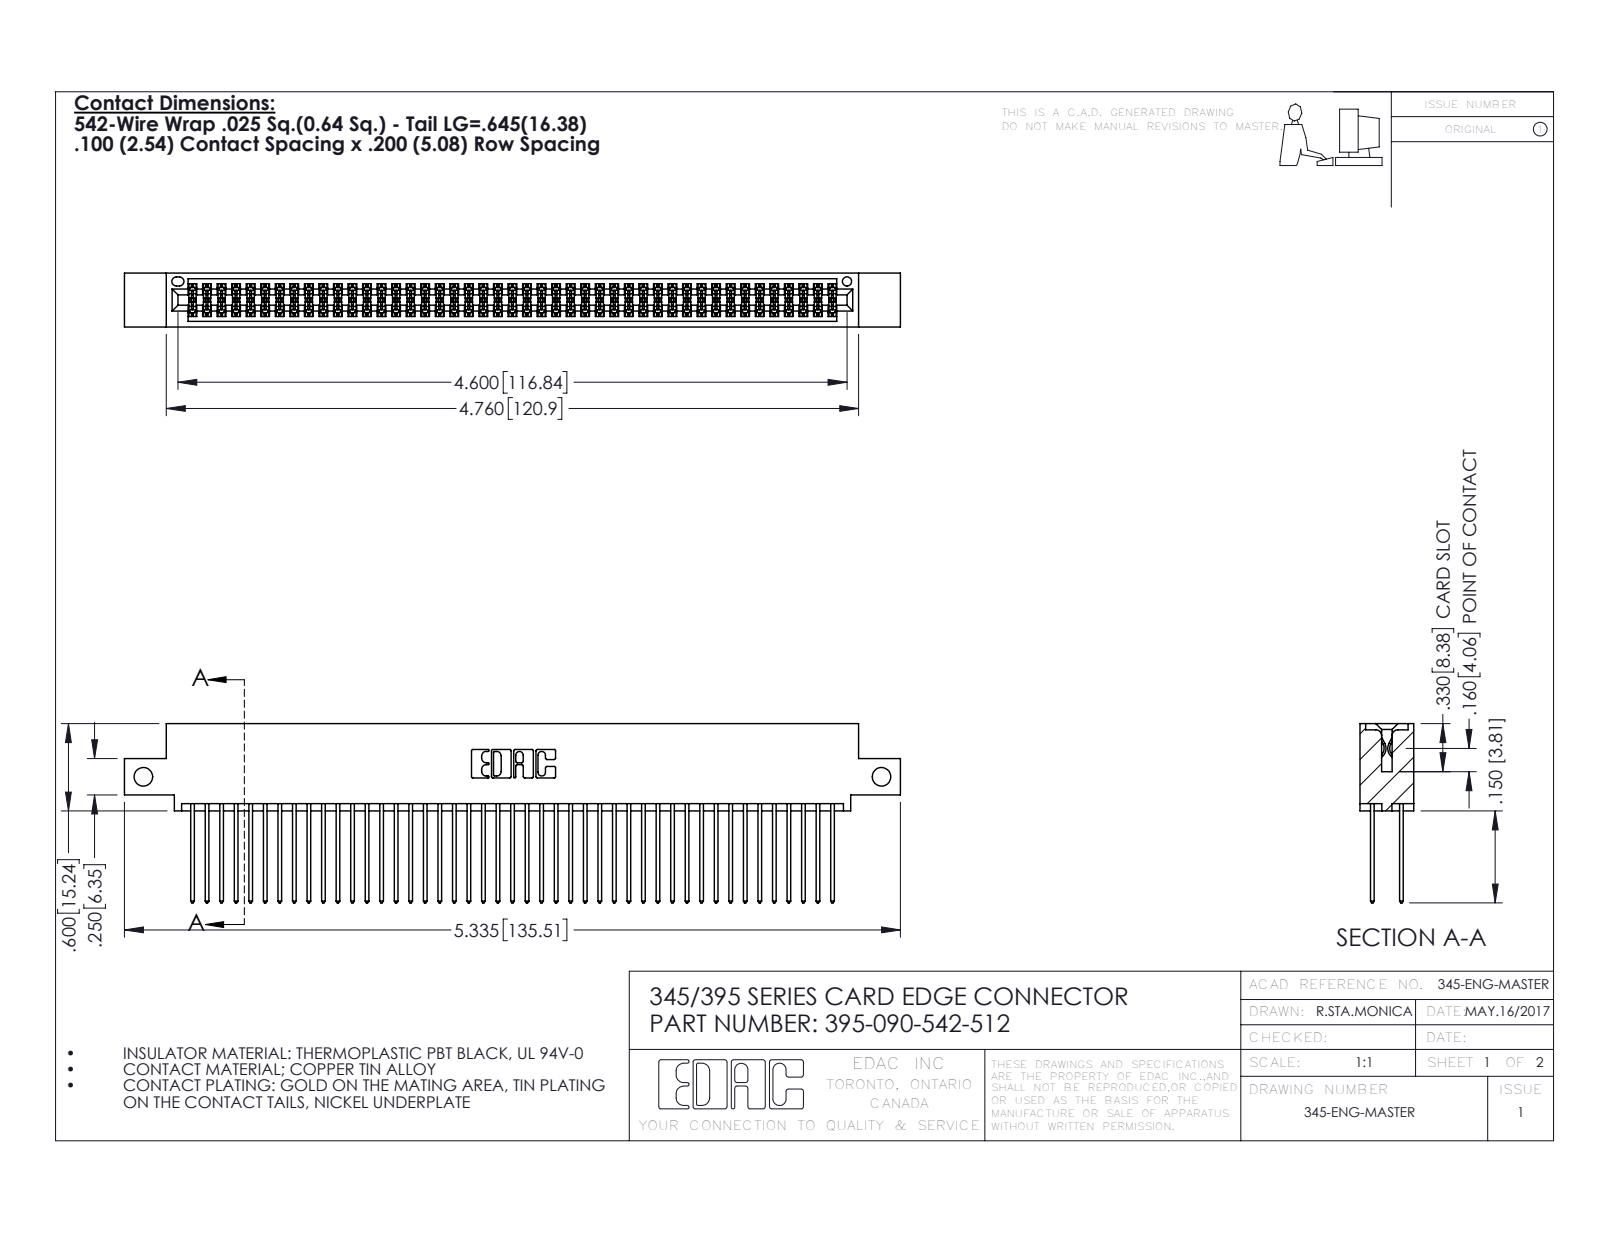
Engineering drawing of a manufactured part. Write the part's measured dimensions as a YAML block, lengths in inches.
part_name: "395-090-542-512; 345 Part_0.110 Offset - Side Mount; 345-292-001_345-293-142"
step_written_by: "SolidWorks 2016 (CONFIG_CONTROL_DESIGN)"
units: inches
bodies: {solids: 91, faces: 4630, planar: 3054, cylindrical: 1576, other: 0}
overall_size: [5.335, 1.232, 0.37]
volume: 0.821
surface_area: 33.88
round_holes:
  - {diameter: 0.128, count: 2}
  - {diameter: 0.064, count: 1}
partial_cylinders:
  - {radius: 0.006, count: 135}
  - {radius: 0.01, count: 90}
  - {radius: 0.01, count: 22}
  - {radius: 0.007, count: 6}
  - {radius: 0.031, count: 6}
  - {radius: 0.026, count: 3}
  - {radius: 0.014, count: 2}
  - {radius: 0.019, count: 2}
face_to_face_distances: [0.298, 0.072, 0.2, 0.098, 0.272, 0.025, 0.225, 0.37, 0.175, 0.149]
hole_center_spacings: [5.075]
